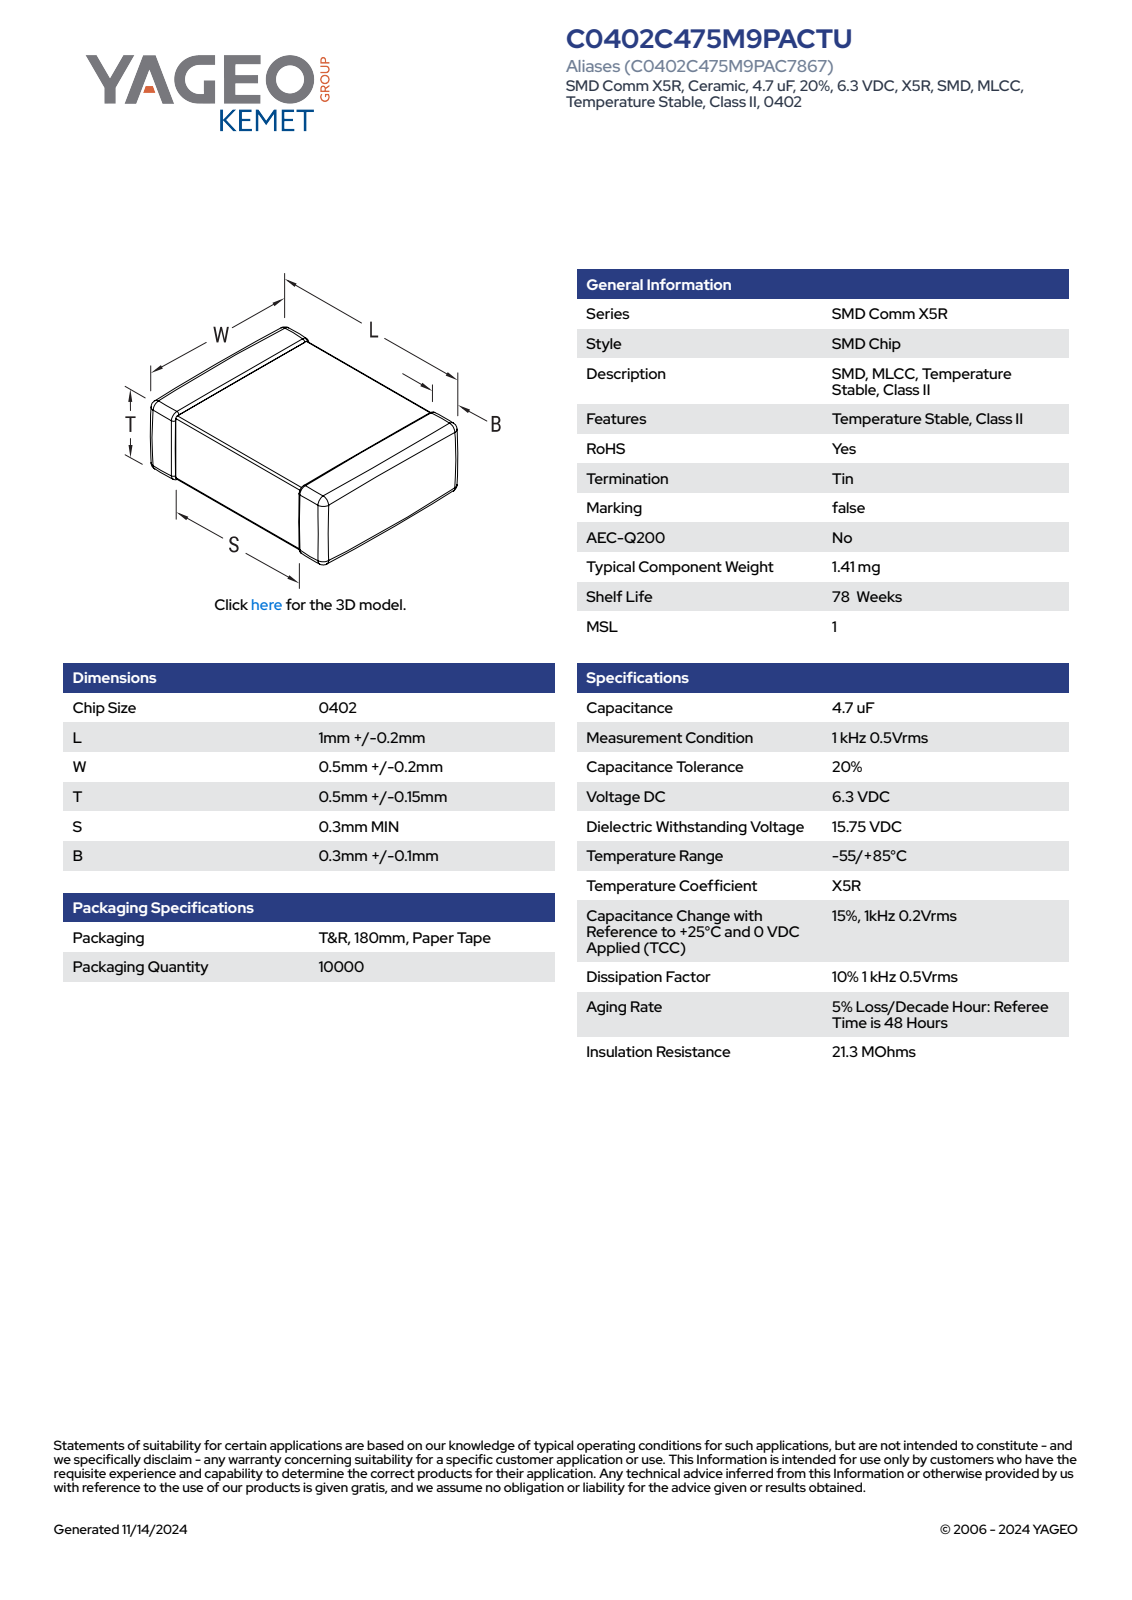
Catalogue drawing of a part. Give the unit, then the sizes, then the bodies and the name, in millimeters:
Units: millimetres
Overall size (bounding box): 1.2 × 0.7 × 0.65
Main face-to-face distances: 0.64, 0.69, 1.2, 0.63, 0.65, 0.68, 0.7, 0.55, 0.6, 0.42
Volume: 0.522 mm³ · Surface area: 4 mm²
Bodies: 4 solids, 125 faces (71 planar, 38 cylindrical, 16 other)
Part name (STEP PRODUCT): CCS_CCSTD_0402_L1.2W0.7T0.65B0.3
STEP written by: SolidWorks 2014 (AUTOMOTIVE_DESIGN)
